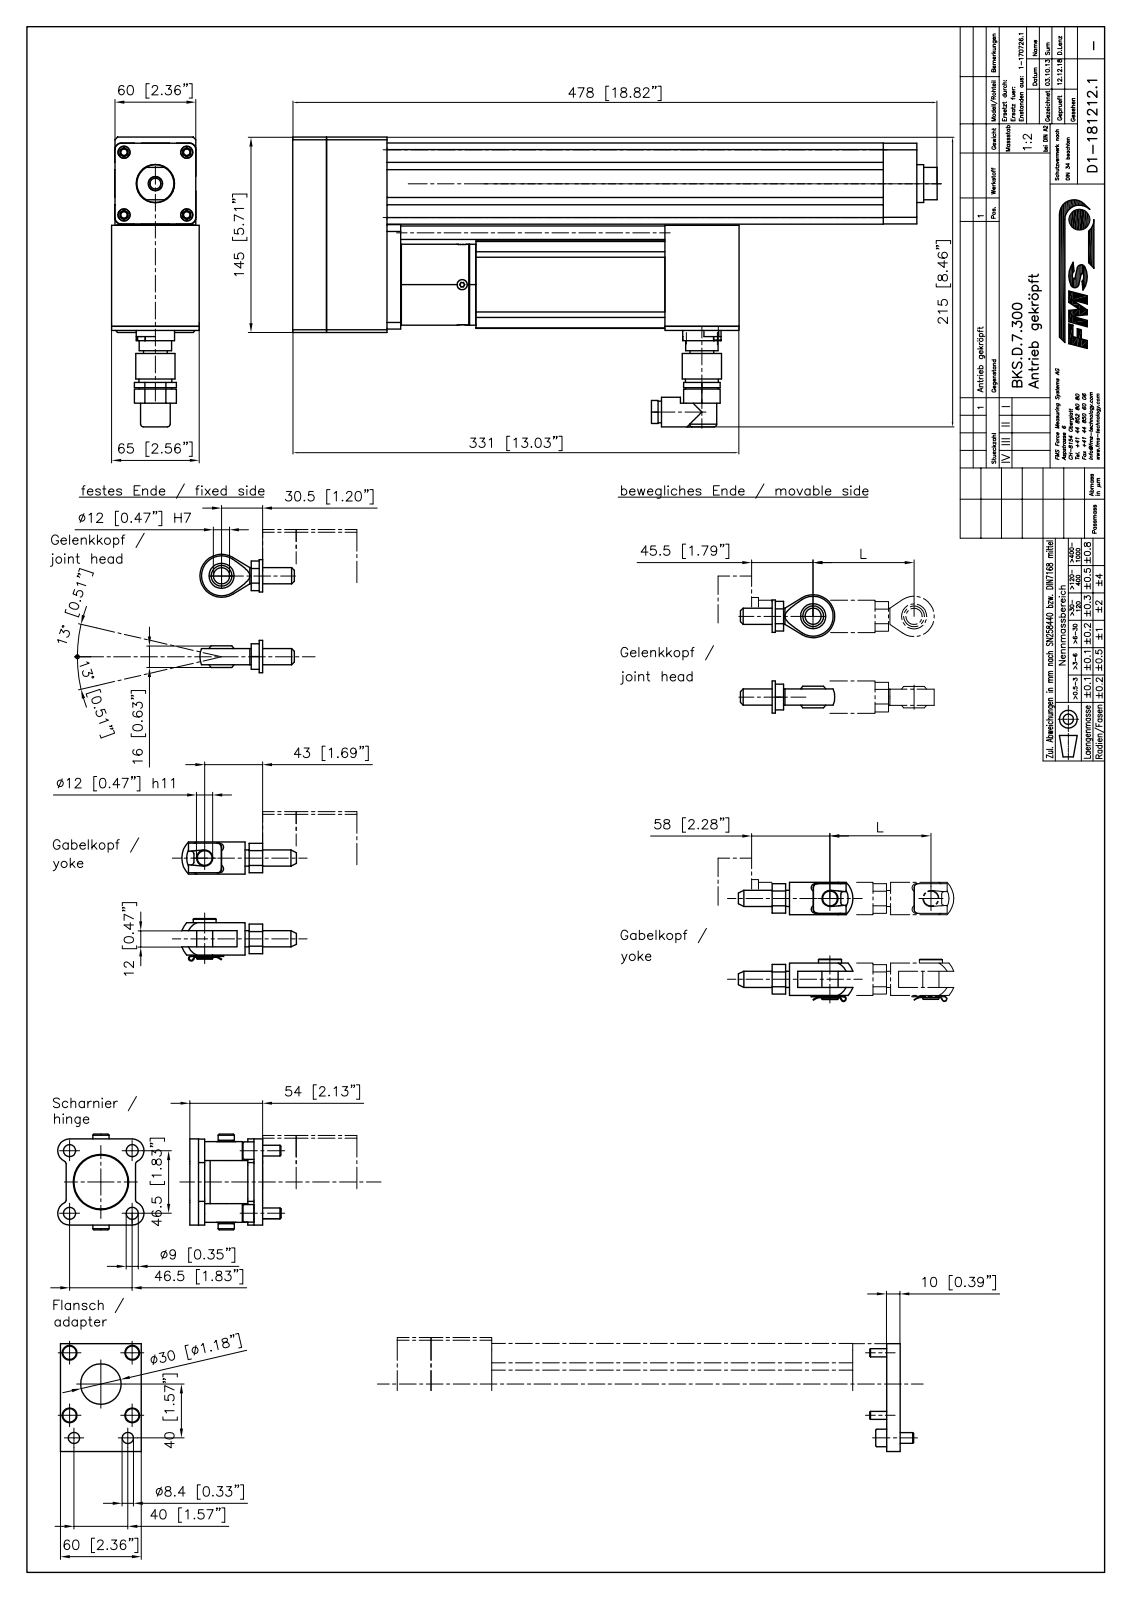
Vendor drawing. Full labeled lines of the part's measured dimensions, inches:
Part name (STEP PRODUCT): K1812121_STP; K1309121; K0702222; K0909182 (+8 more)
STEP written by: Mechanical Desktop 2009 (CONFIG_CONTROL_DESIGN)
Units: inches
Bodies: 39 solids, 1158 faces (423 planar, 498 cylindrical, 237 other)
Overall size (bounding box): 22.48 × 8.465 × 2.559
Volume: 118.9 in³ · Surface area: 834.1 in²
Round holes (diameter × count): ⌀0.135 ×8, ⌀0.203 ×8, ⌀0.217 ×8, ⌀0.102 ×6, ⌀0.394 ×5, ⌀0.134 ×4, ⌀0.165 ×4, ⌀0.177 ×4, ⌀0.209 ×4, ⌀0.248 ×4, ⌀0.252 ×4, ⌀0.262 ×4
Round bosses / shafts (diameter × count): ⌀0.315 ×8, ⌀0.236 ×8, ⌀0.197 ×8, ⌀0.085 ×7, ⌀0.118 ×6, ⌀0.394 ×5, ⌀0.945 ×2, ⌀0.217 ×2
Partial cylindrical surfaces — rounded edges, fillets, slot ends (radius × count): R0.197 ×19, R0.02 ×14, R0.016 ×12, R0.027 ×12, R0.118 ×8, R0.177 ×8, R0.079 ×6, R0.787 ×5
Main face-to-face distances: 2.374, 2.368, 0.098, 2.165, 0.093, 2.461, 2.467, 0.059, 2.756, 2.559
Hole centre spacings: 0.727, 0.932, 1.53, 1.676, 2.16, 0.524, 0.787, 1.024
